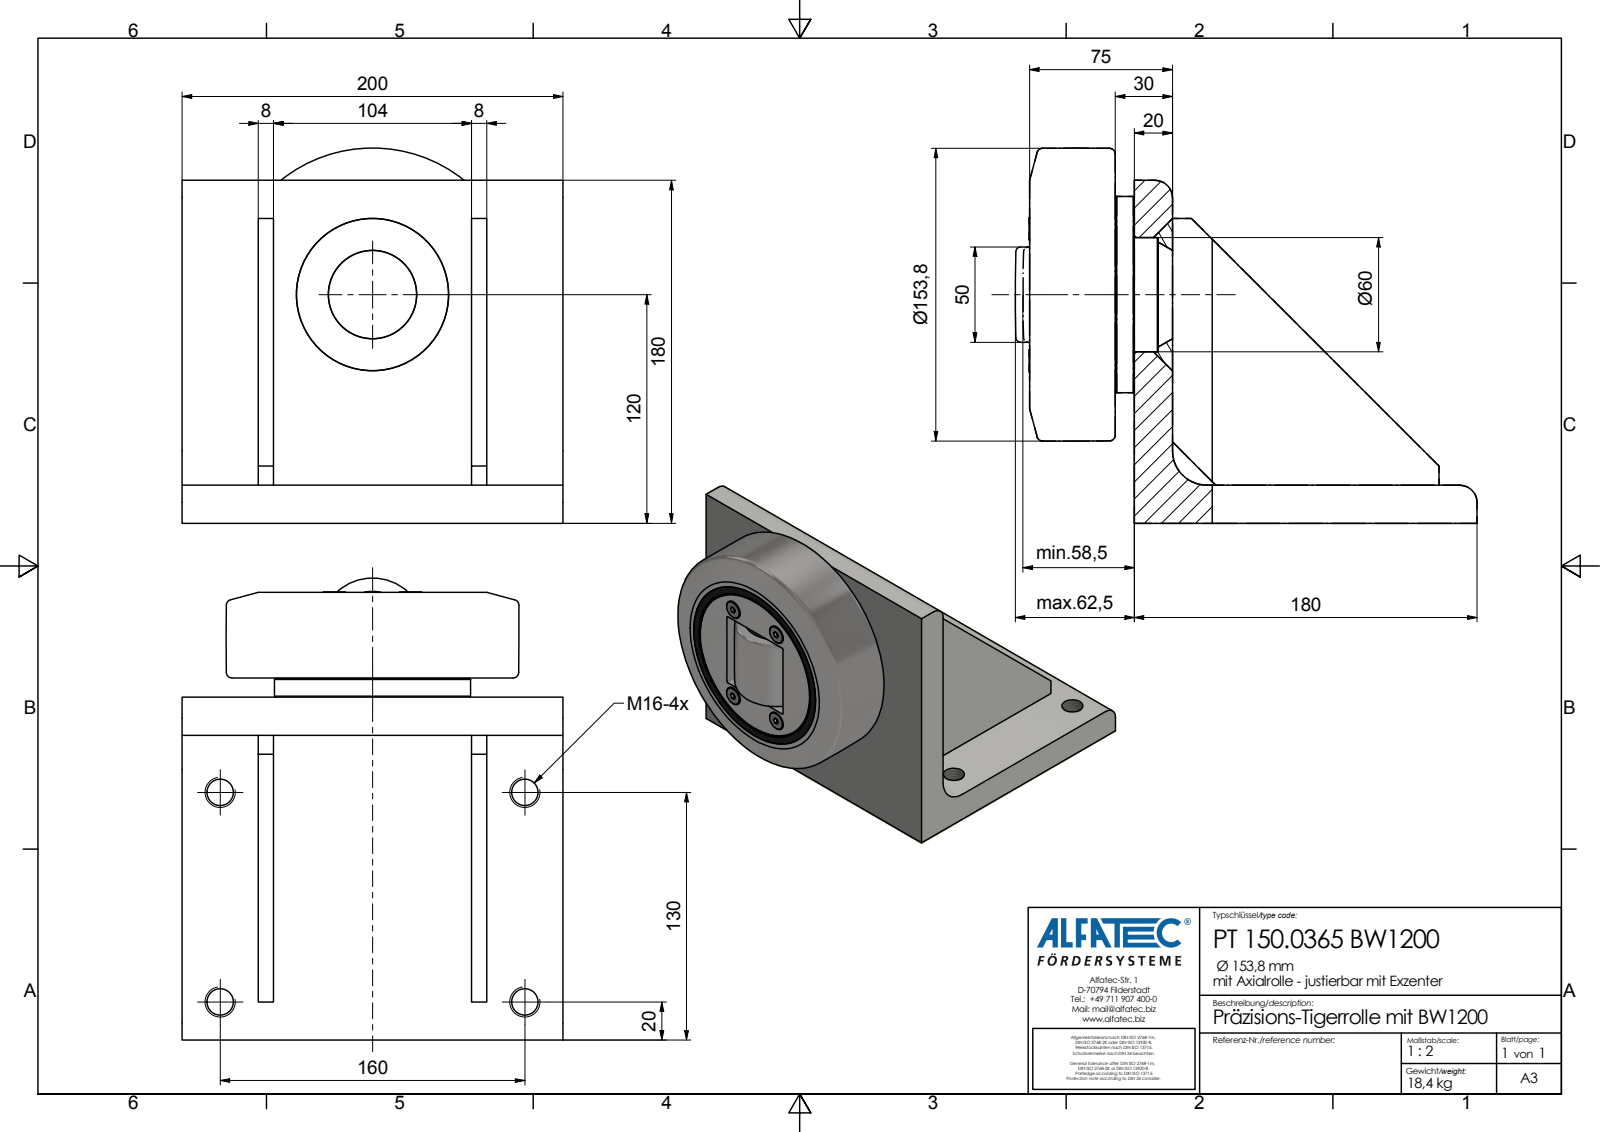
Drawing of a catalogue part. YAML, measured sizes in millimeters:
part_name: "PT 150.0365 BW1200_Kontur"
step_written_by: "Autodesk Inventor 2020 (AP242_MANAGED_MODEL_BASED_3D_ENGINEERING_MIM_LF)"
units: millimeters
bodies: {solids: 1, faces: 87, planar: 61, cylindrical: 17, other: 9}
overall_size: [242.5, 200, 196.9]
volume: 2439000
surface_area: 244337
round_holes:
  - {diameter: 13.84, count: 4}
round_bosses_or_shafts:
  - {diameter: 11.7, count: 4}
  - {diameter: 103, count: 1}
  - {diameter: 101.4, count: 1}
partial_cylinders:
  - {radius: 9, count: 2}
  - {radius: 18, count: 1}
  - {radius: 20.4, count: 1}
  - {radius: 20.5, count: 1}
face_to_face_distances: [20, 8, 112, 160, 40, 48, 152, 104, 120, 75]
hole_center_spacings: [110, 160, 194.16]
